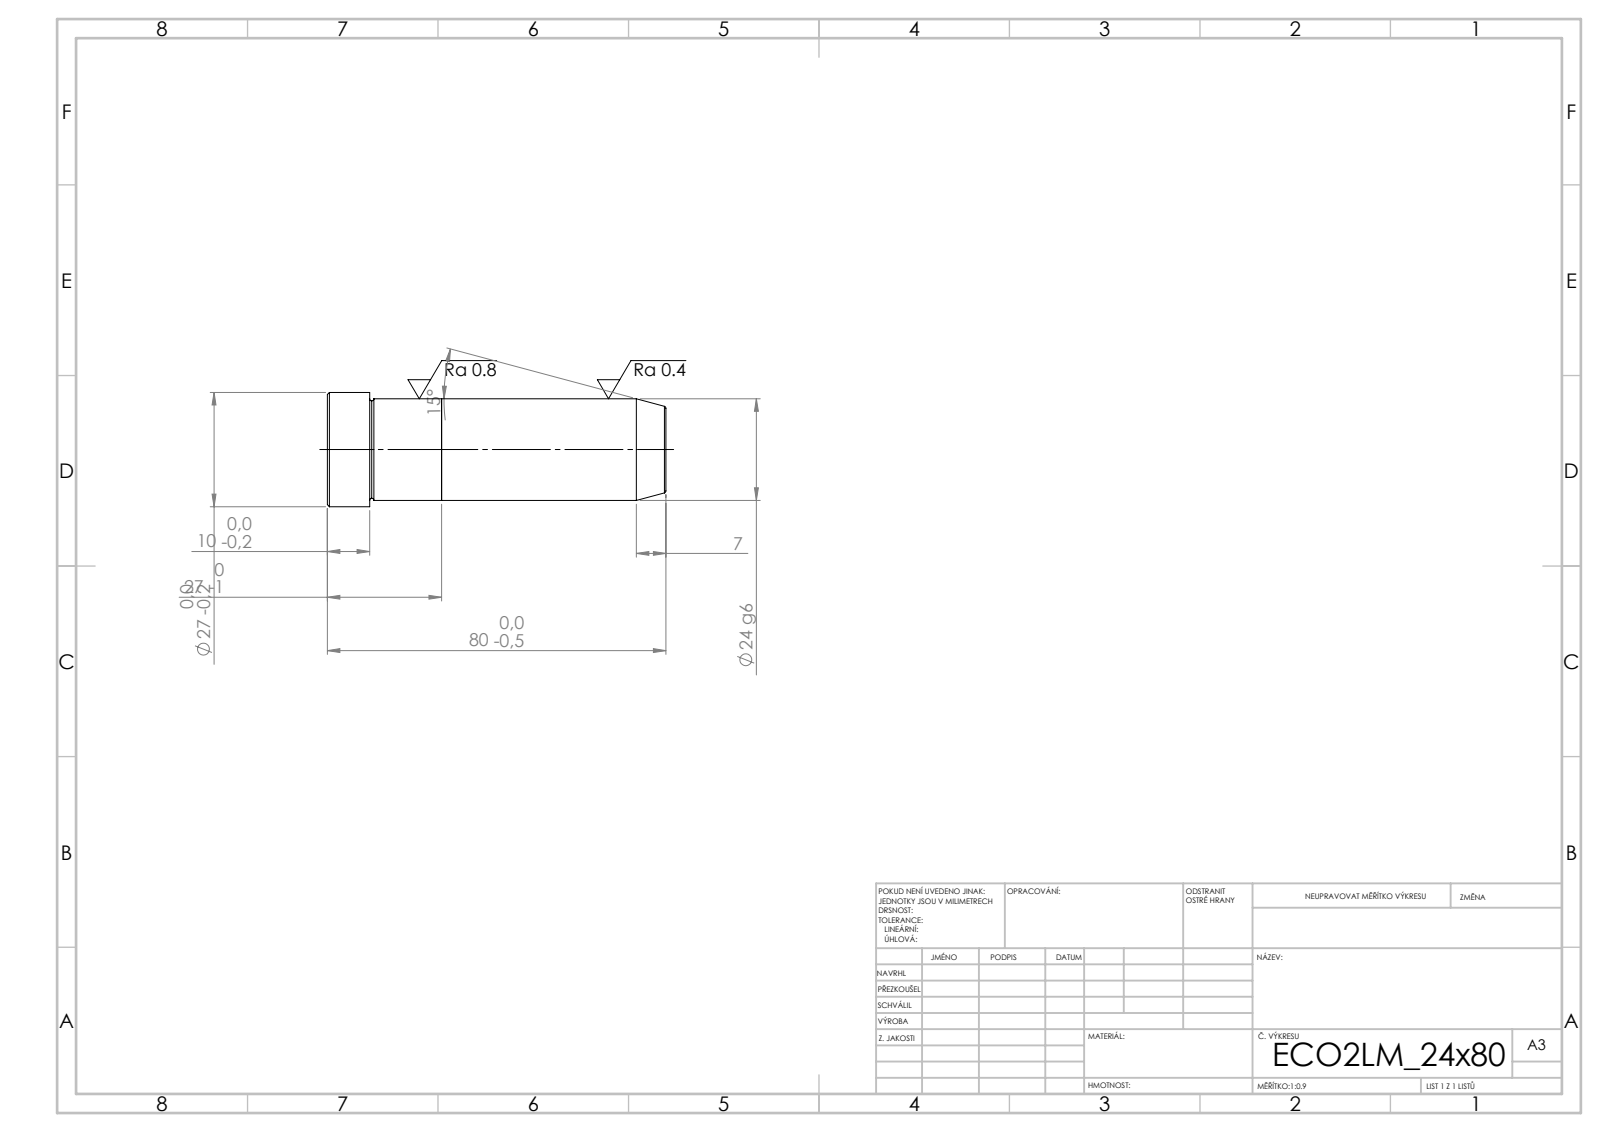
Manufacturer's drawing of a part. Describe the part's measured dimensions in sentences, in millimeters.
Its 3-D file was written by "SolidWorks 2019 (CONFIG_CONTROL_DESIGN)". It is 2 solids with 21 faces: 5 planar, 6 cylindrical and 10 other. Overall it measures 80 by 27 by 27 millimeters. Its volume is 36 882 cubic millimeters and its surface area 8 029 square millimeters. Round bosses or shafts: 1 of diameter 27, 1 of diameter 24. The main face-to-face distances are 27, 53, 80, 70, 17, 10.
